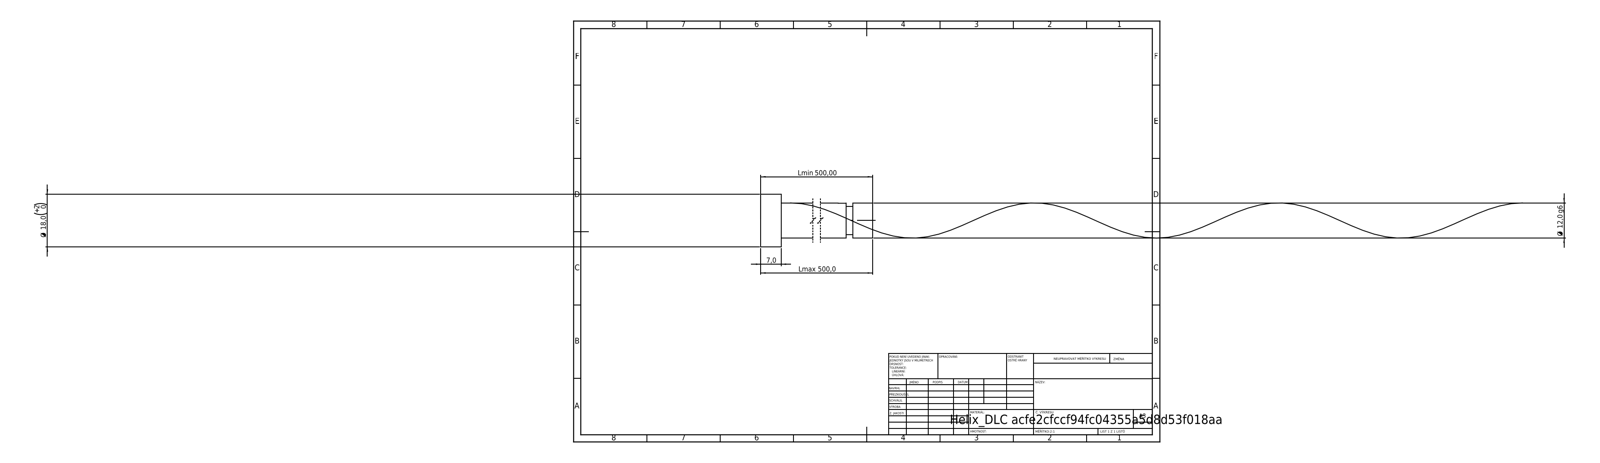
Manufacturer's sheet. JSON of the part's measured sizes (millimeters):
{"step_written_by": "SolidWorks 2019 (CONFIG_CONTROL_DESIGN)", "units": "millimeters", "bodies": {"solids": 1, "faces": 21, "planar": 6, "cylindrical": 14, "other": 1}, "overall_size": [500, 18, 18], "volume_mm3": 56899, "surface_area_mm2": 19876, "round_bosses_or_shafts": [[18, 1], [12, 1], [9.6, 1]], "face_to_face_distances": [7, 500, 493, 493.35, 486.35, 6.65, 490.95, 483.95, 2.4, 9.05]}
